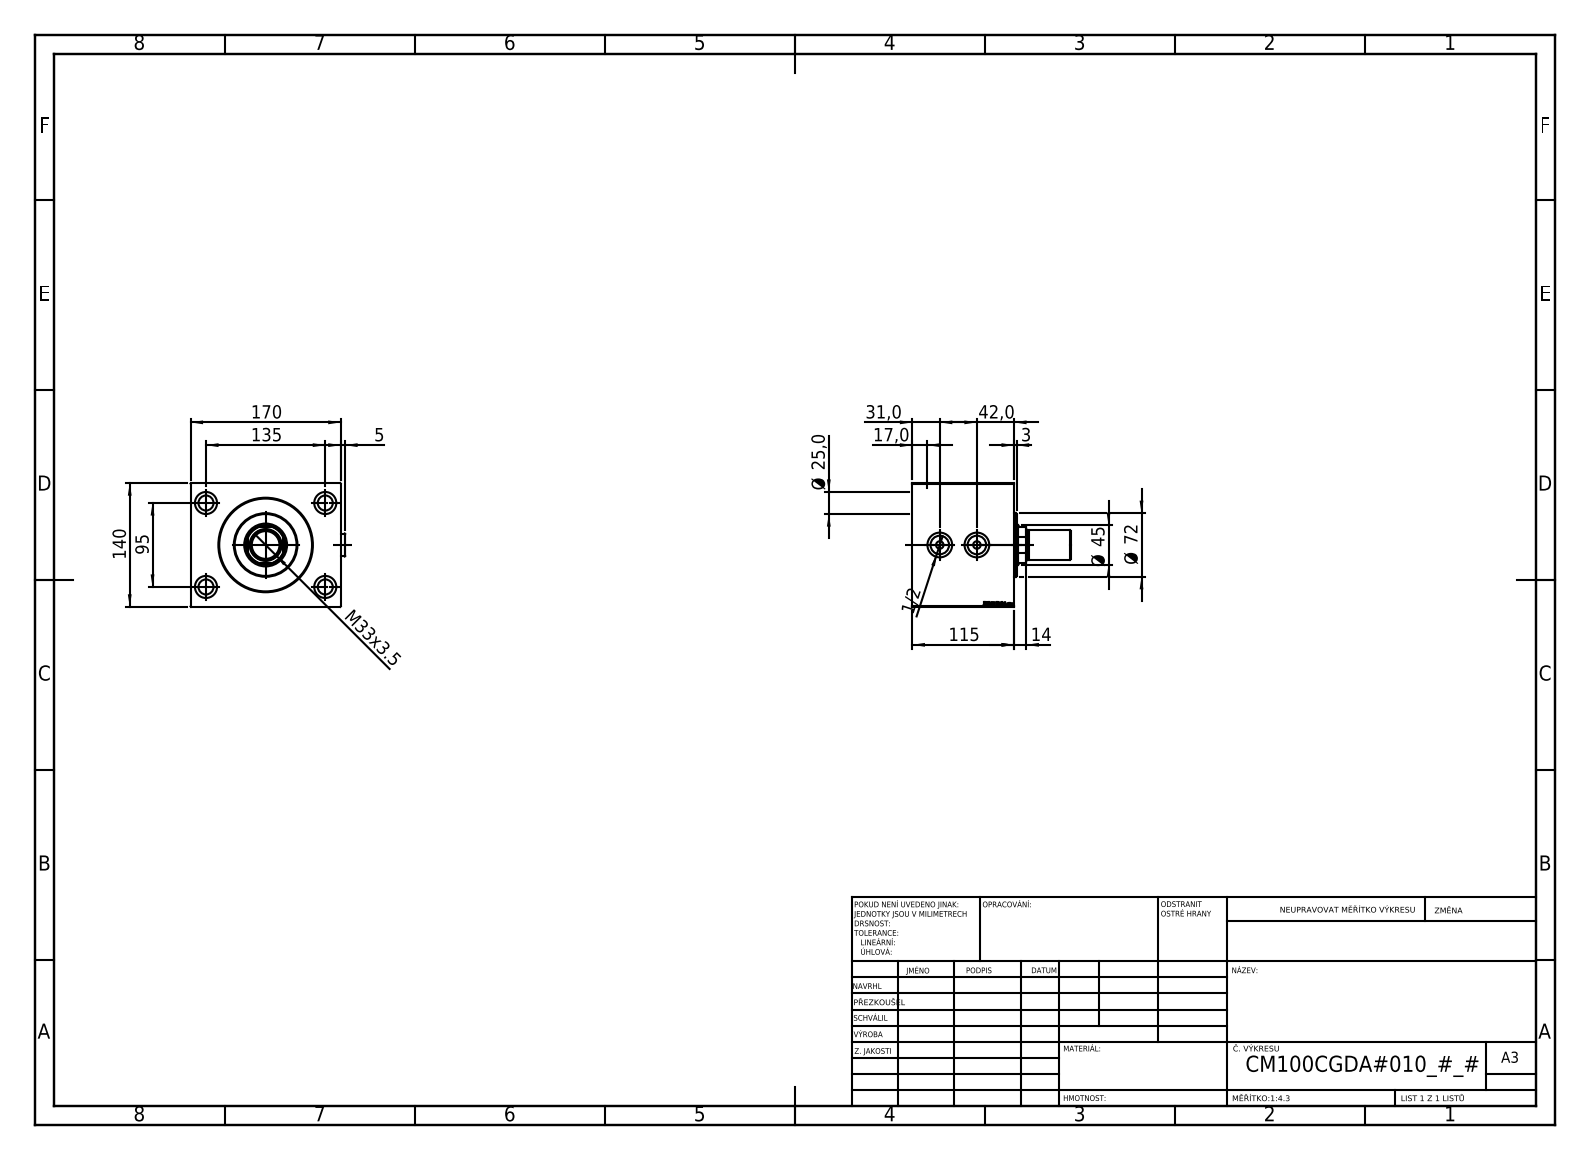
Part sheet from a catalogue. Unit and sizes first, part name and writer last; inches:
Units: inches
Overall size (bounding box): 7.047 × 6.886 × 5.512
Round holes (diameter × count): ⌀0.669 ×4, ⌀0.984 ×4, ⌀0.335 ×2, ⌀0.825 ×2, ⌀1.102 ×2, ⌀1.24 ×1, ⌀1.772 ×1, ⌀1.909 ×1, ⌀3.937 ×1, ⌀4.016 ×1, ⌀4.134 ×1
Round bosses / shafts (diameter × count): ⌀1.024 ×2, ⌀2.835 ×1, ⌀1.299 ×1, ⌀1.22 ×1
Partial cylindrical surfaces — rounded edges, fillets, slot ends (radius × count): R0.866 ×1
Main face-to-face distances: 5.512, 4.528, 2.52, 2.008, 6.693, 0.85, 1.157, 3.677, 0.394, 1.244
Hole centre spacings: 3.25, 3.74, 5.315, 6.499, 1.654
Volume: 155.5 in³ · Surface area: 367 in²
Bodies: 6 solids, 931 faces (447 planar, 80 cylindrical, 404 other)
Part name (STEP PRODUCT): V450CM_C_Body; V450CM_MALE_METRIC; Zatka_OIL_PORT; V450CM_C_VCP (+1 more)
STEP written by: SolidWorks 2019 (CONFIG_CONTROL_DESIGN)
